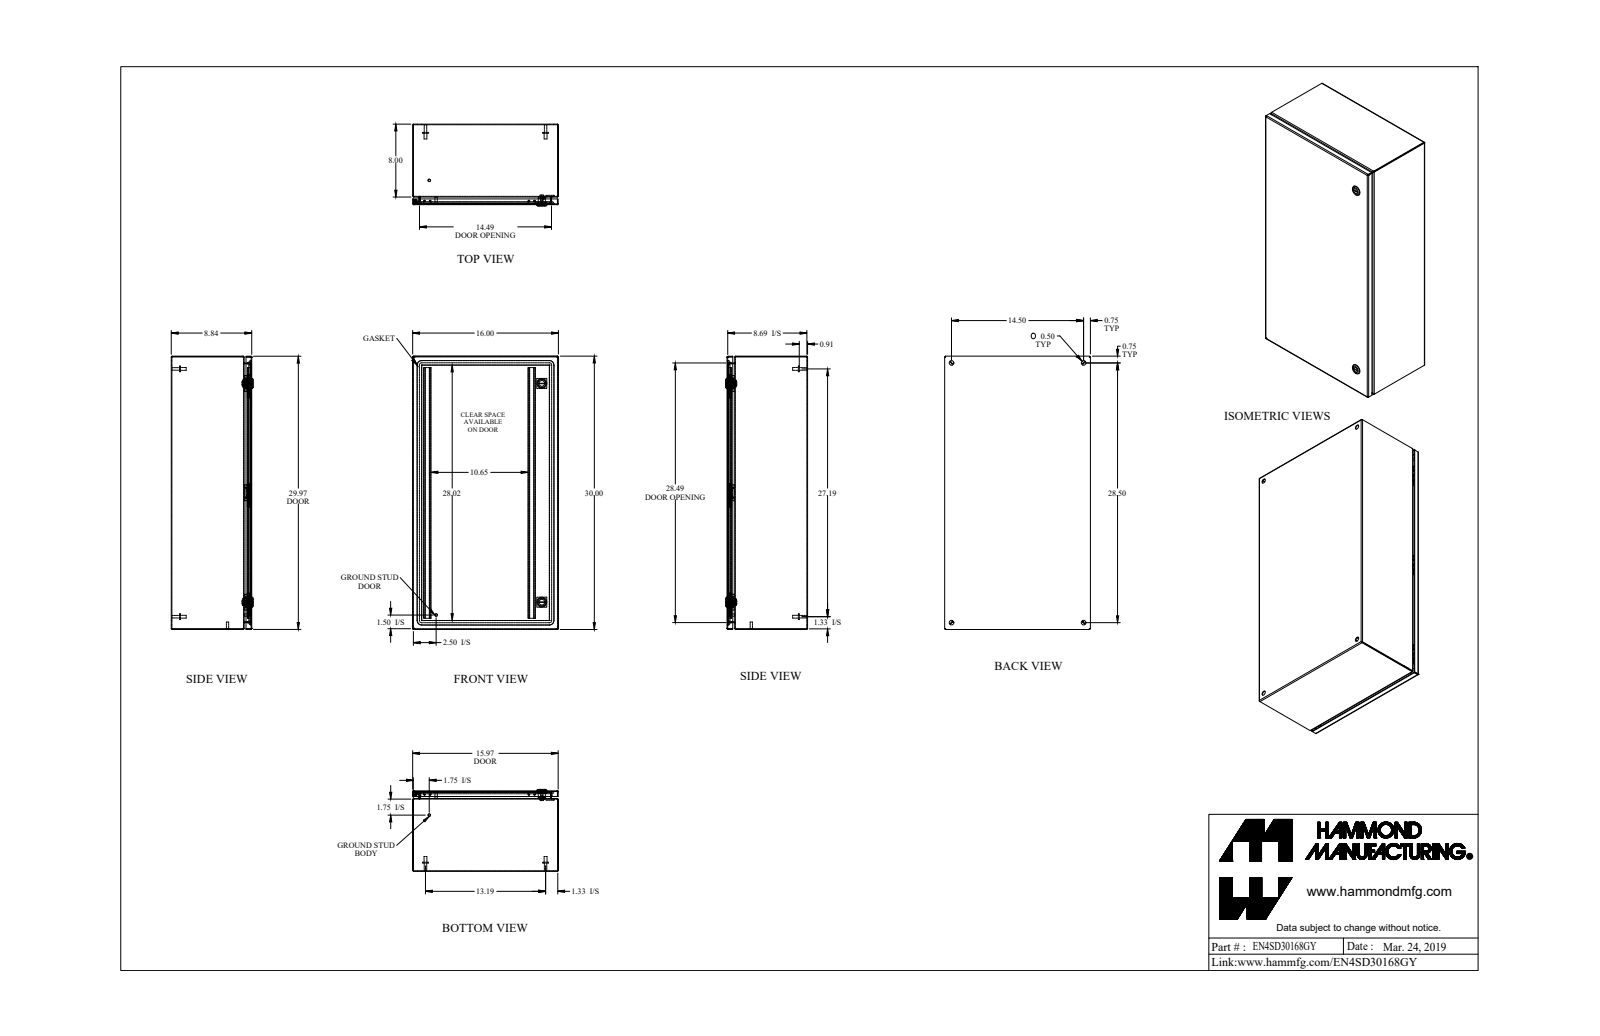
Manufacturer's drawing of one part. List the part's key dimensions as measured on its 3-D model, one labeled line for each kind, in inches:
Part name (STEP PRODUCT): EN4SD30168GY_Default
STEP written by: SolidWorks 2019 (CONFIG_CONTROL_DESIGN)
Units: inches
Bodies: 31 solids, 885 faces (422 planar, 295 cylindrical, 168 other)
Overall size (bounding box): 30 × 16 × 8.997
Volume: 148.1 in³ · Surface area: 4 173 in²
Round holes (diameter × count): ⌀0.5 ×4, ⌀0.232 ×2, ⌀0.625 ×2, ⌀0.785 ×2, ⌀0.172 ×1, ⌀0.24 ×1, ⌀0.242 ×1
Round bosses / shafts (diameter × count): ⌀0.625 ×4, ⌀0.313 ×4, ⌀0.27 ×4, ⌀1.1 ×2, ⌀0.525 ×2, ⌀0.281 ×2, ⌀0.25 ×2, ⌀0.455 ×1
Partial cylindrical surfaces — rounded edges, fillets, slot ends (radius × count): R0.036 ×20, R0.108 ×20, R0.043 ×12, R0.081 ×12, R0.382 ×12, R19.003 ×8, R0.006 ×6, R0.062 ×6
Main face-to-face distances: 0.072, 8.765, 8.693, 8.837, 15.928, 29.928, 15.856, 16, 29.856, 30
Hole centre spacings: 13.615, 14.5, 28.5, 31.976, 2.493, 2.494, 23.999, 26.271
